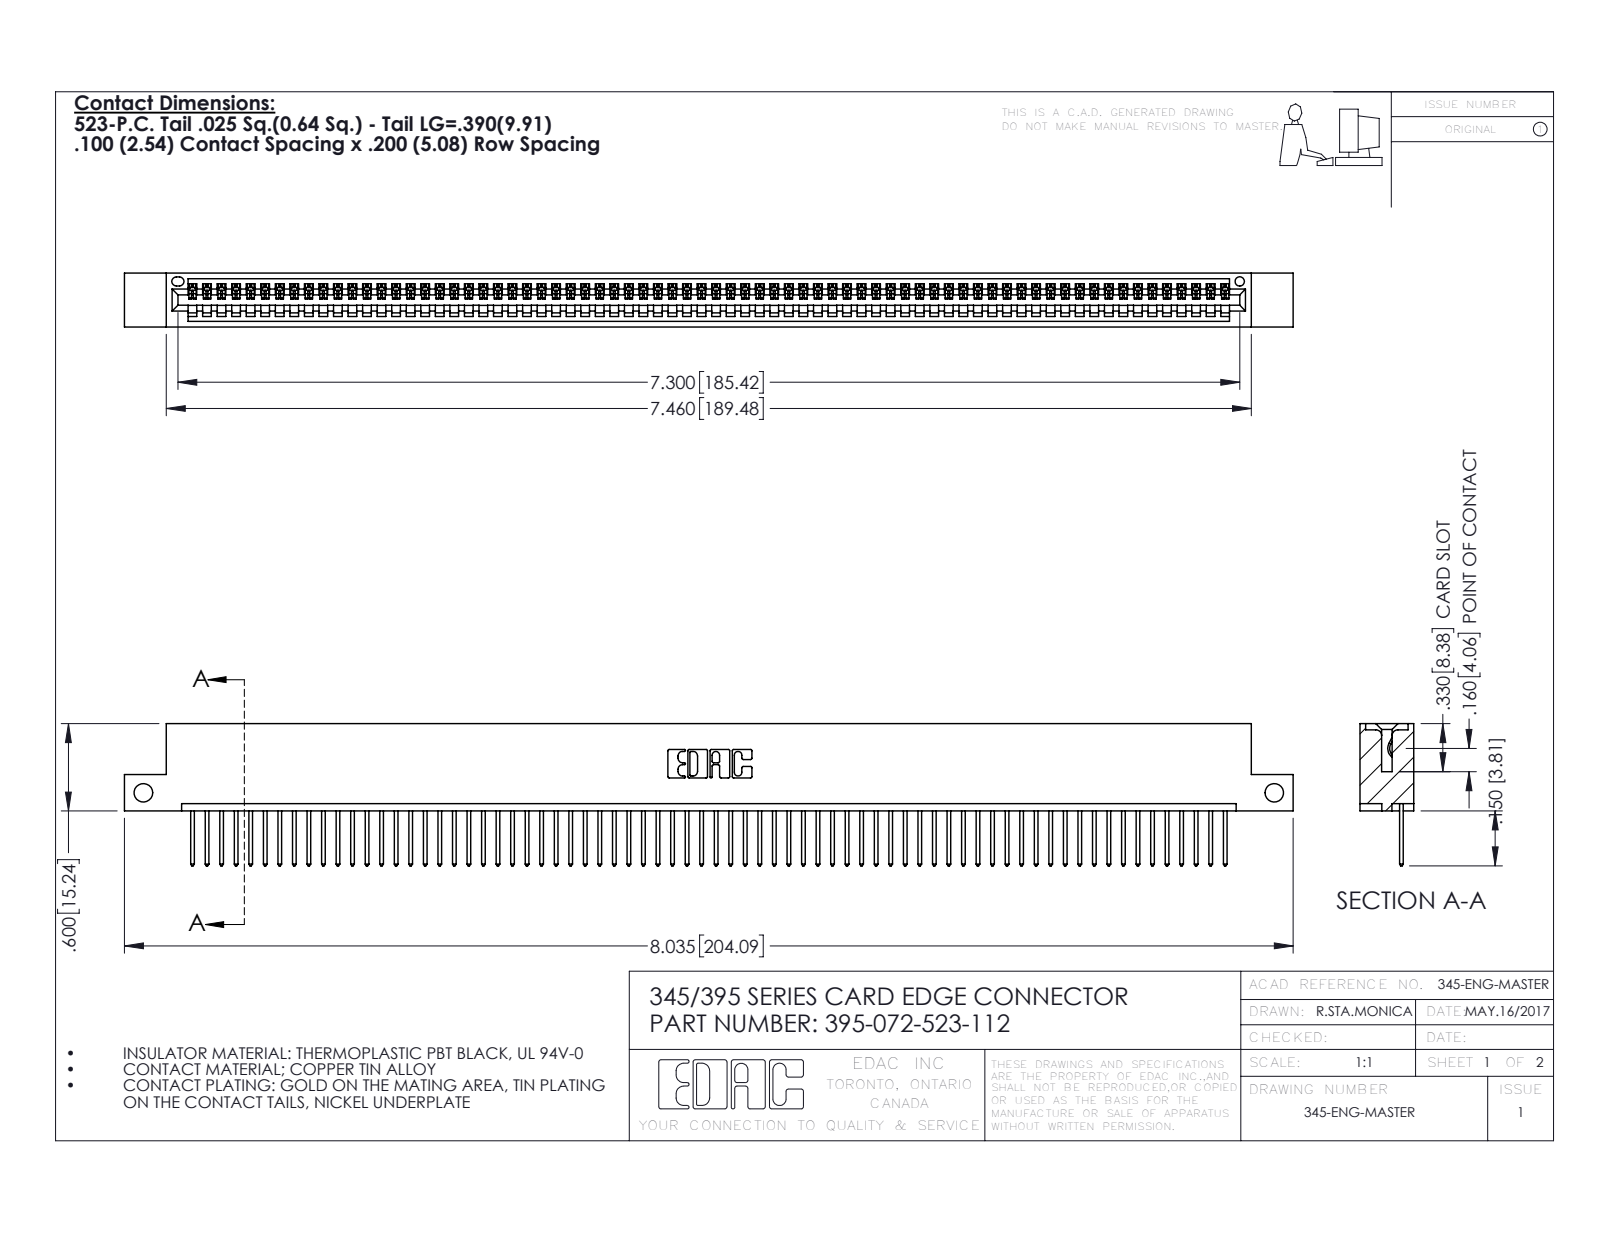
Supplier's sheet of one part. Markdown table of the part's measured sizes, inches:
| quantity | value |
| --- | --- |
| part name | 345-292-001_345-293-123; 345 Part_Flush Mounting Lugs - Side Mount; 395-072-523-112 |
| STEP written by | SolidWorks 2016 (CONFIG_CONTROL_DESIGN) |
| units | inches |
| bodies | 73 solids, 4302 faces (2960 planar, 1342 cylindrical, 0 other) |
| overall size | 8.035 × 0.977 × 0.37 |
| volume | 1.191 in³ |
| surface area | 40.73 in² |
| round holes (diameter × count) | 0.128 × 2, 0.064 × 1 |
| partial cylindrical surfaces (radius × count) | 0.006 × 144, 0.01 × 144, 0.01 × 22, 0.007 × 6, 0.031 × 6, 0.026 × 3, 0.031 × 2, 0.04 × 2 |
| main face-to-face distances | 0.298, 0.072, 0.37, 0.2, 0.098, 0.272, 0.025, 0.225, 0.149, 0.072 |
| hole center spacings | 7.775 |
